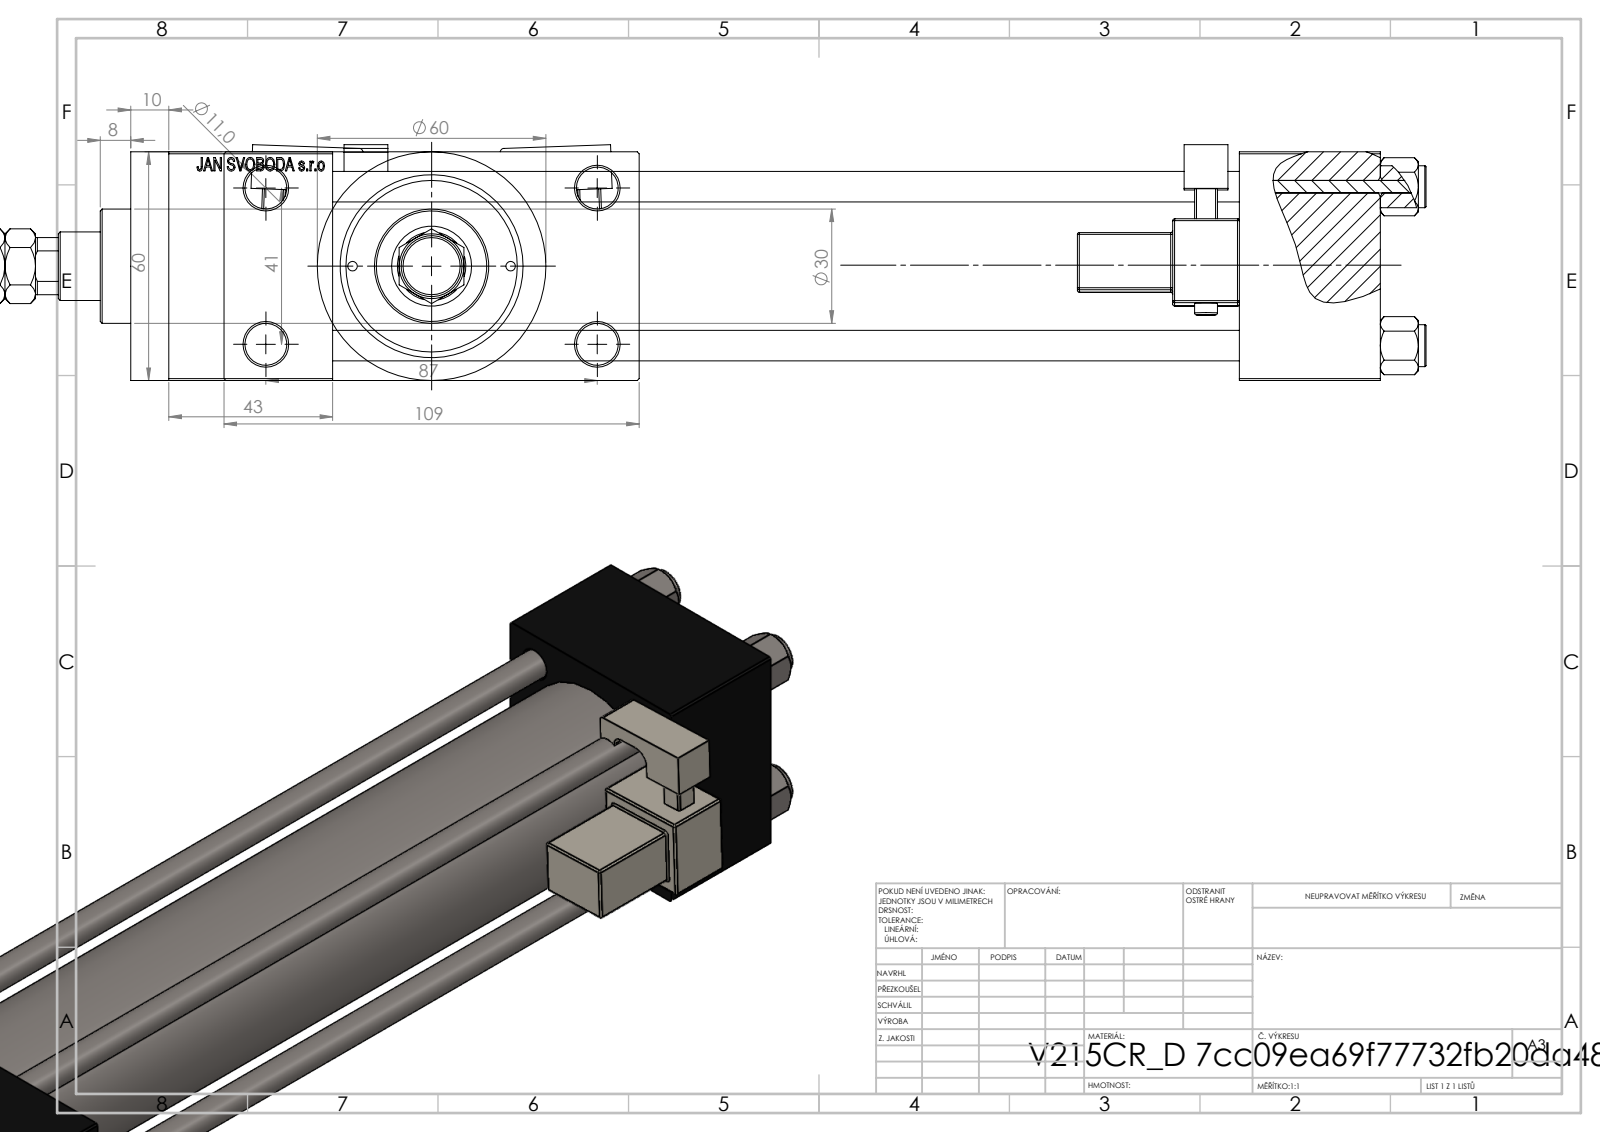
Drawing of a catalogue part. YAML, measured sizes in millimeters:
part_name: "NUT_M5_D; V215CR_D_TYCINKA; V215CR_MSU; V215_VC_A (+3 more)"
step_written_by: "SolidWorks 2019 (CONFIG_CONTROL_DESIGN)"
units: millimeters
bodies: {solids: 14, faces: 1318, planar: 574, cylindrical: 156, other: 588}
overall_size: [393, 109, 61.9]
volume: 713516
surface_area: 213562
round_holes:
  - {diameter: 8, count: 4}
  - {diameter: 11, count: 4}
  - {diameter: 2.5, count: 2}
  - {diameter: 7, count: 2}
  - {diameter: 16.66, count: 2}
  - {diameter: 24, count: 2}
  - {diameter: 8.5, count: 1}
  - {diameter: 18, count: 1}
  - {diameter: 21, count: 1}
  - {diameter: 31, count: 1}
  - {diameter: 40, count: 1}
  - {diameter: 45, count: 1}
round_bosses_or_shafts:
  - {diameter: 11, count: 4}
  - {diameter: 6, count: 2}
  - {diameter: 60, count: 1}
  - {diameter: 46, count: 1}
  - {diameter: 30, count: 1}
  - {diameter: 16, count: 1}
  - {diameter: 10, count: 1}
partial_cylinders:
  - {radius: 0.5, count: 48}
  - {radius: 1, count: 2}
  - {radius: 2.5, count: 2}
  - {radius: 4, count: 2}
  - {radius: 8.5, count: 1}
face_to_face_distances: [60, 238, 24.5, 84.5, 37, 275, 318, 281, 43, 109]
hole_center_spacings: [20.85, 22.65, 29.49, 30.62, 41.7, 46.53, 47.15, 48.09]
